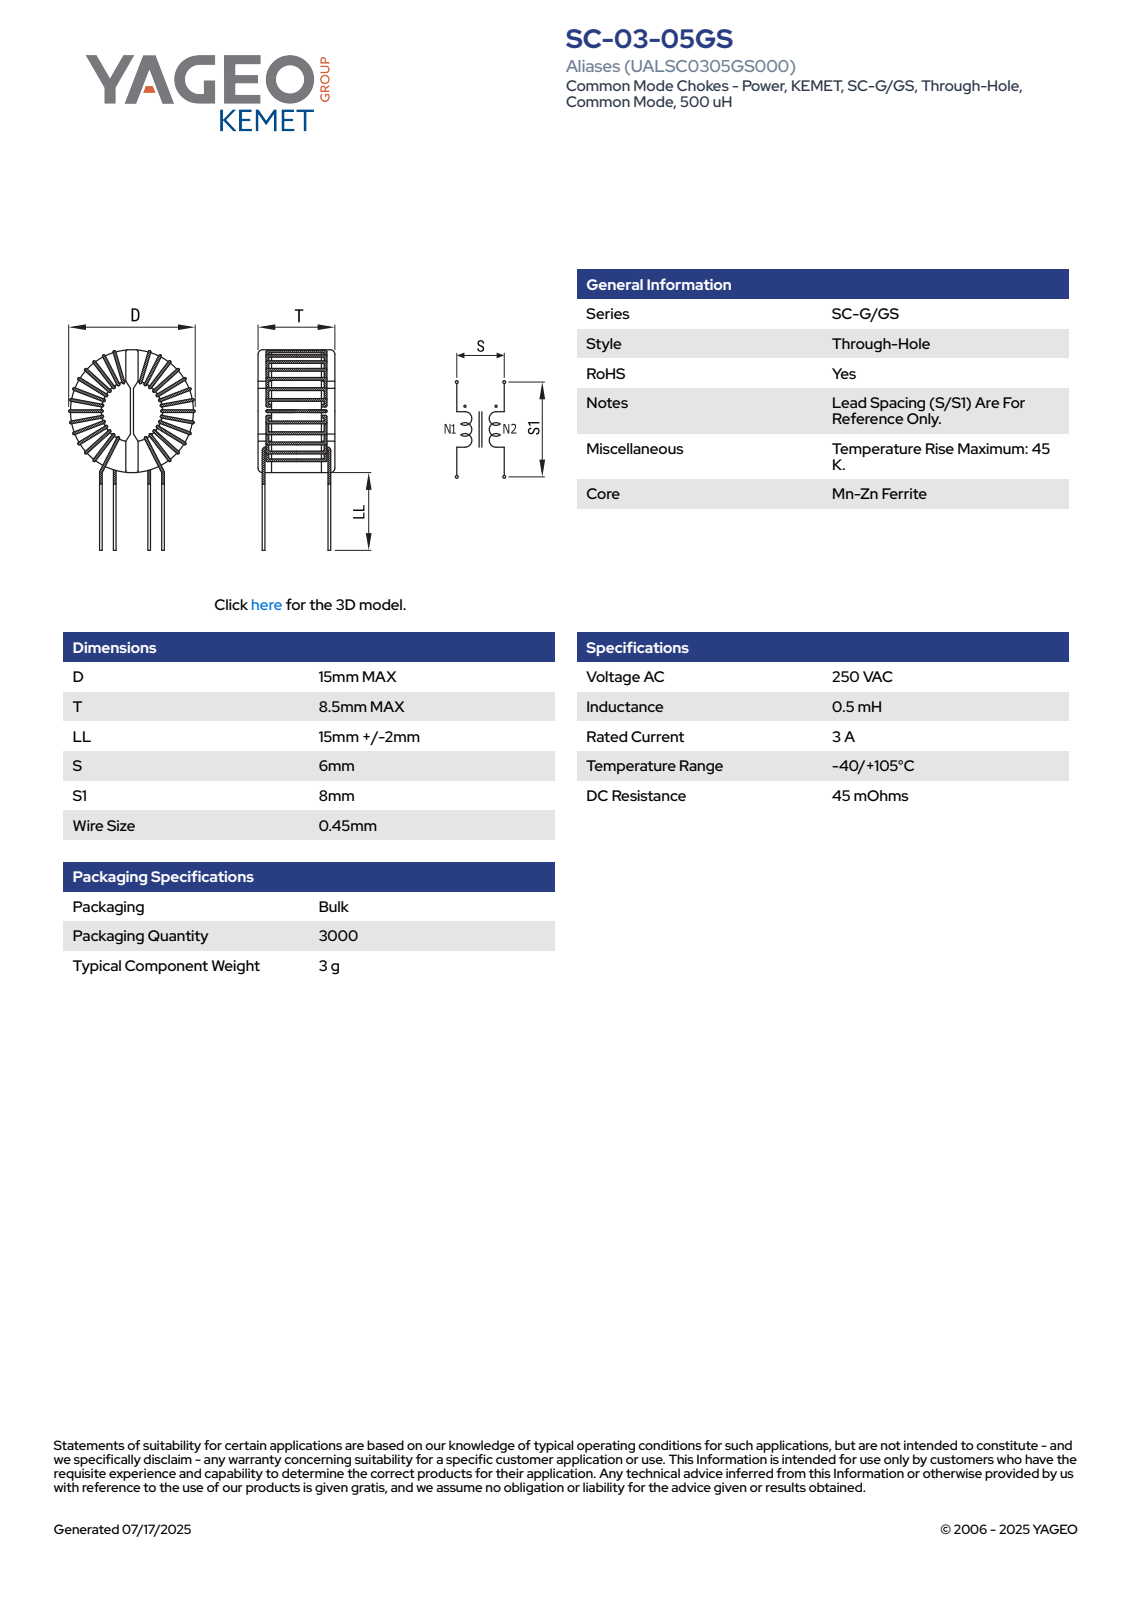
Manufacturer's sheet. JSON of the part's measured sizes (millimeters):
{"part_name": "FR11_6_3_MAX(TYP); SC_KEMET Logo_12.1; SC-03-05GS; FR211CU(CASE)_MAX (+1 more)", "step_written_by": "SolidWorks 2018 (AUTOMOTIVE_DESIGN)", "units": "millimeters", "bodies": {"solids": 8, "faces": 262, "planar": 107, "cylindrical": 82, "other": 73}, "overall_size": [28.37, 15, 8.5], "volume_mm3": 1264, "surface_area_mm2": 2102, "round_holes": [[5.35, 1], [6, 1], [11.2, 1], [11.7, 1]], "round_bosses_or_shafts": [[0.45, 8], [12.2, 1], [11, 1], [5.85, 1]], "partial_cylinders_radius": [[0.23, 16], [2.13, 1], [2.42, 1], [6.05, 1], [6.1, 1], [7.5, 1]], "face_to_face_distances": [0.5, 3.5, 2.7, 3, 1.4, 0.8, 0.85, 1.9, 4.9, 5.4]}
